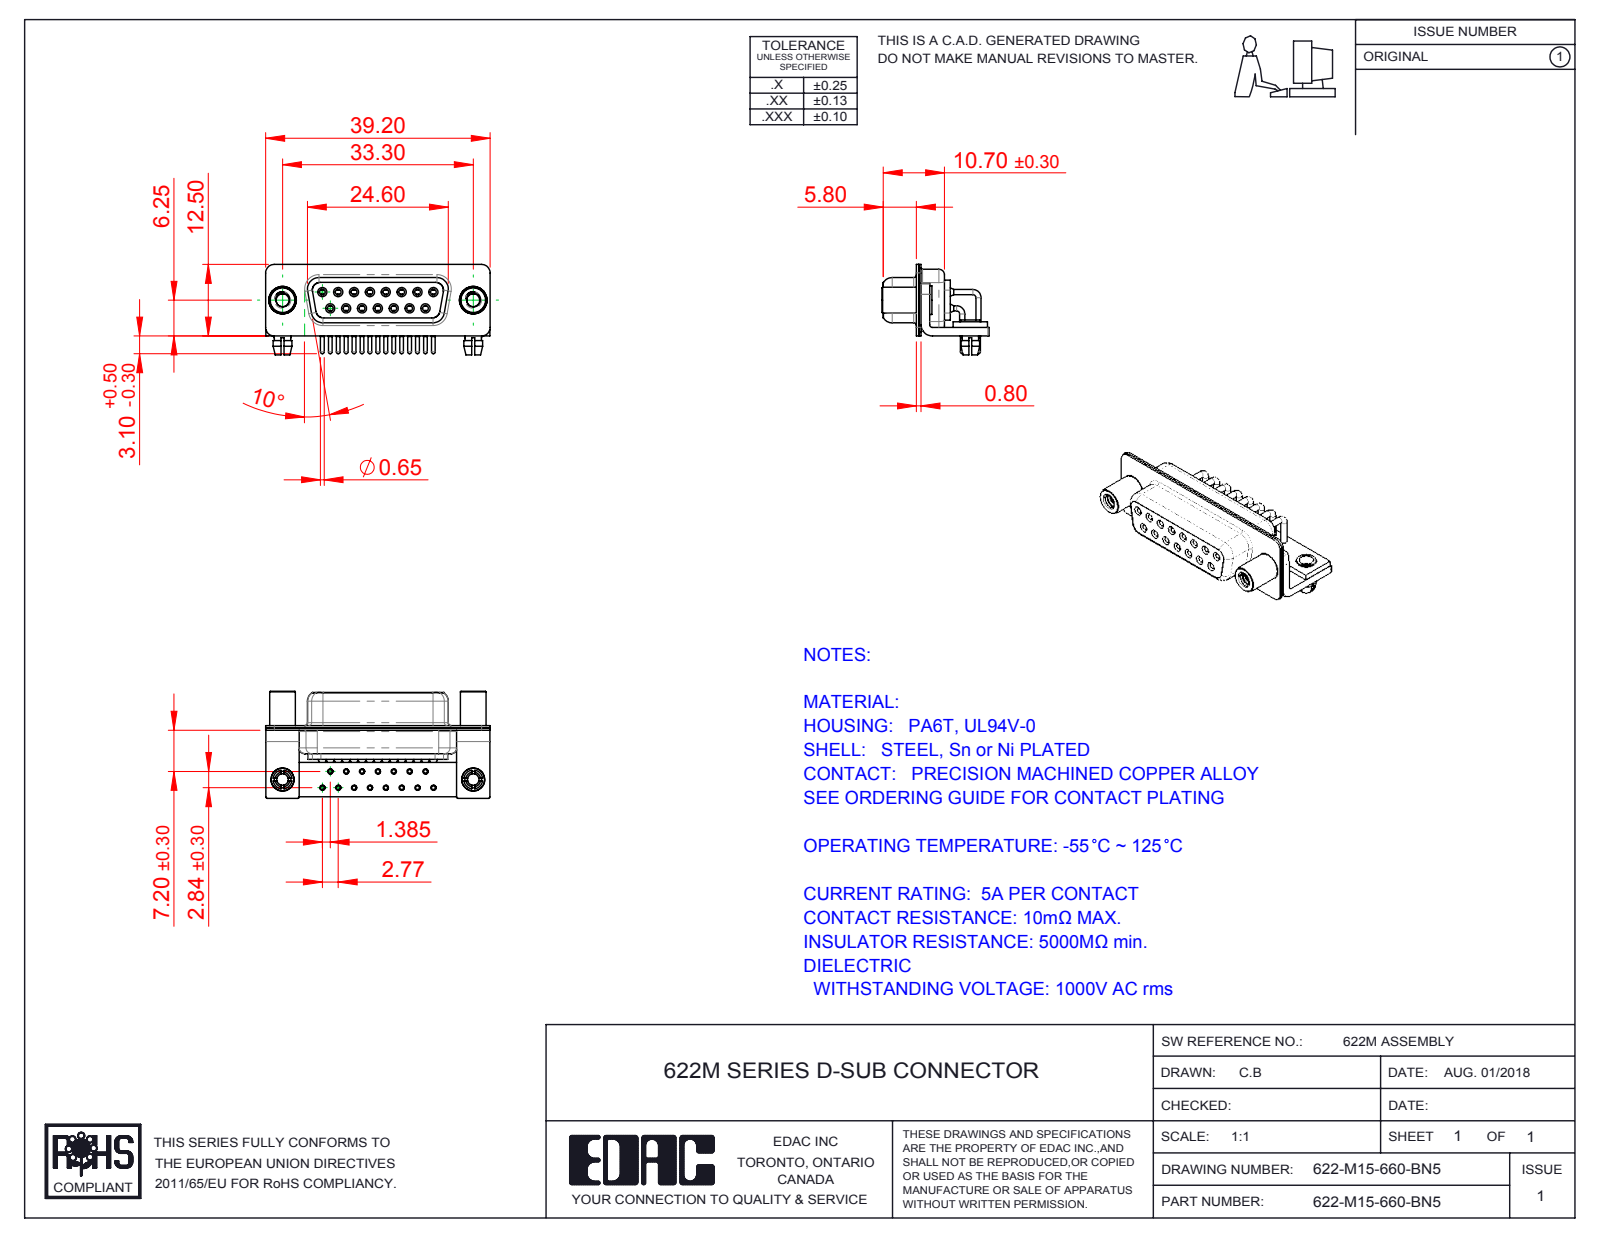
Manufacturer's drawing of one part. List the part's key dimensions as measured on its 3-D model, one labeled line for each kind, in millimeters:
Part name (STEP PRODUCT): 622M Stabilizer Bracket; 622M Contact Row 2; 622M Contact Row 1; 622M Shell Rear_15 Contacts (+6 more)
STEP written by: SolidWorks 2016 (CONFIG_CONTROL_DESIGN)
Units: millimetres
Bodies: 25 solids, 1296 faces (368 planar, 608 cylindrical, 320 other)
Overall size (bounding box): 39.2 × 18.7 × 15.8
Volume: 3 146 mm³ · Surface area: 8 070 mm²
Round holes (diameter × count): ⌀2 ×17, ⌀0.9 ×15, ⌀1 ×15, ⌀1.1 ×15, ⌀1.7 ×15, ⌀1.8 ×15, ⌀2.26 ×2, ⌀2.5 ×2, ⌀3.2 ×2, ⌀4 ×2, ⌀4.8 ×2
Round bosses / shafts (diameter × count): ⌀0.9 ×22, ⌀1.6 ×15, ⌀1.5 ×15, ⌀0.65 ×15, ⌀5 ×2, ⌀4.9 ×2, ⌀4.5 ×2, ⌀4 ×2
Partial cylindrical surfaces — rounded edges, fillets, slot ends (radius × count): R0.25 ×16, R1.5 ×16, R2 ×13, R1.35 ×8, R1.6 ×8, R0.5 ×5, R0.6 ×4, R0.65 ×4
Main face-to-face distances: 0.4, 2.3, 1.9, 0.8, 9.35, 1.5, 1, 1.45, 8.95, 0.85
Hole centre spacings: 3.16, 2.77, 5.54, 8.31, 11.08, 5.03, 5.04, 7.48
